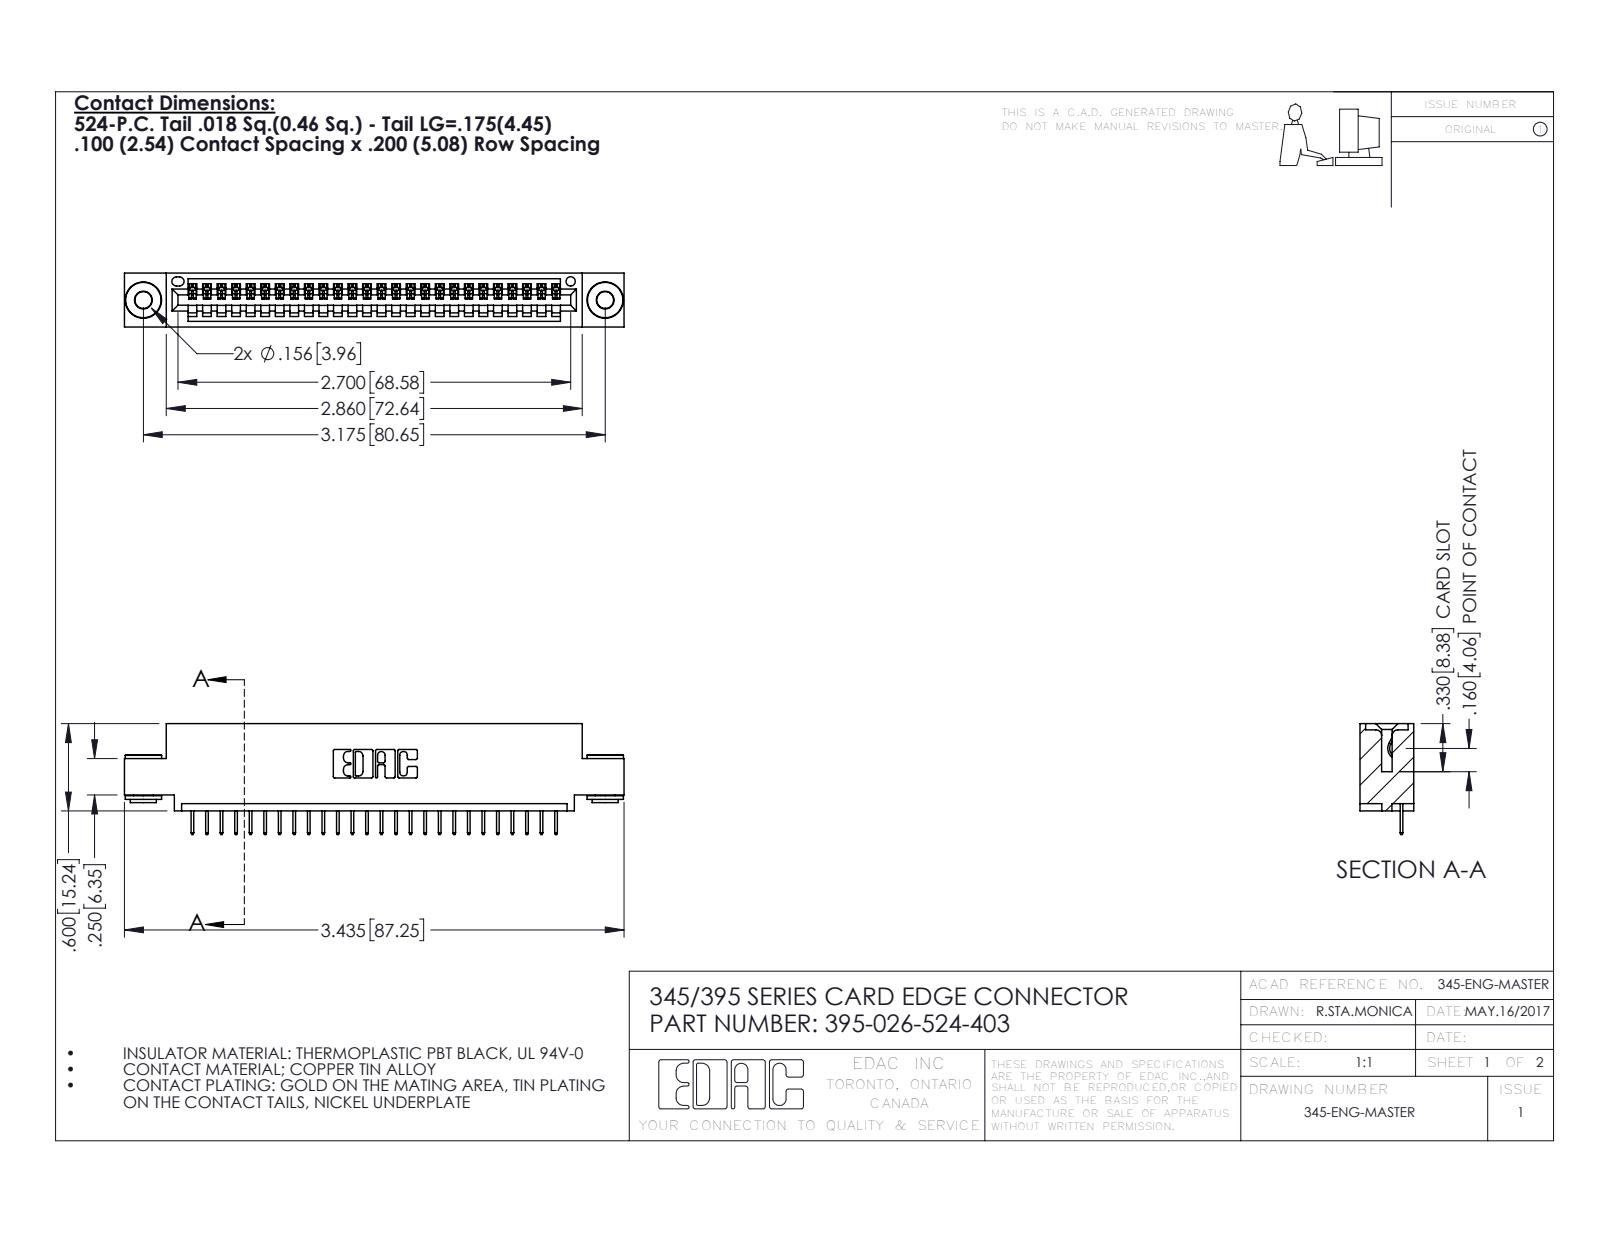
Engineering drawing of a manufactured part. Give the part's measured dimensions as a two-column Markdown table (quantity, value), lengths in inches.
| quantity | value |
| --- | --- |
| part name | 395-026-524-403; 345-292-001_345-293-124; 345 Part_0.110 Offset - 0.156 Dia-TH; 345-250-002_345-250-002-102 |
| STEP written by | SolidWorks 2016 (CONFIG_CONTROL_DESIGN) |
| units | inches |
| bodies | 29 solids, 1780 faces (1290 planar, 482 cylindrical, 8 other) |
| overall size | 3.435 × 0.762 × 0.37 |
| volume | 0.488 in³ |
| surface area | 16.09 in² |
| round holes (diameter × count) | 0.116 × 2, 0.156 × 2, 0.064 × 1 |
| round bosses / shafts (diameter × count) | 0.25 × 2, 0.18 × 2, 0.136 × 2 |
| partial cylindrical surfaces (radius × count) | 0.006 × 52, 0.01 × 22, 0.007 × 6, 0.031 × 6, 0.026 × 3, 0.031 × 2, 0.04 × 2, 0.014 × 1 |
| main face-to-face distances | 0.072, 0.298, 0.37, 0.2, 0.025, 0.098, 0.272, 0.225, 0.072, 0.149 |
| hole center spacings | 0.27, 2.94, 3.175 |
